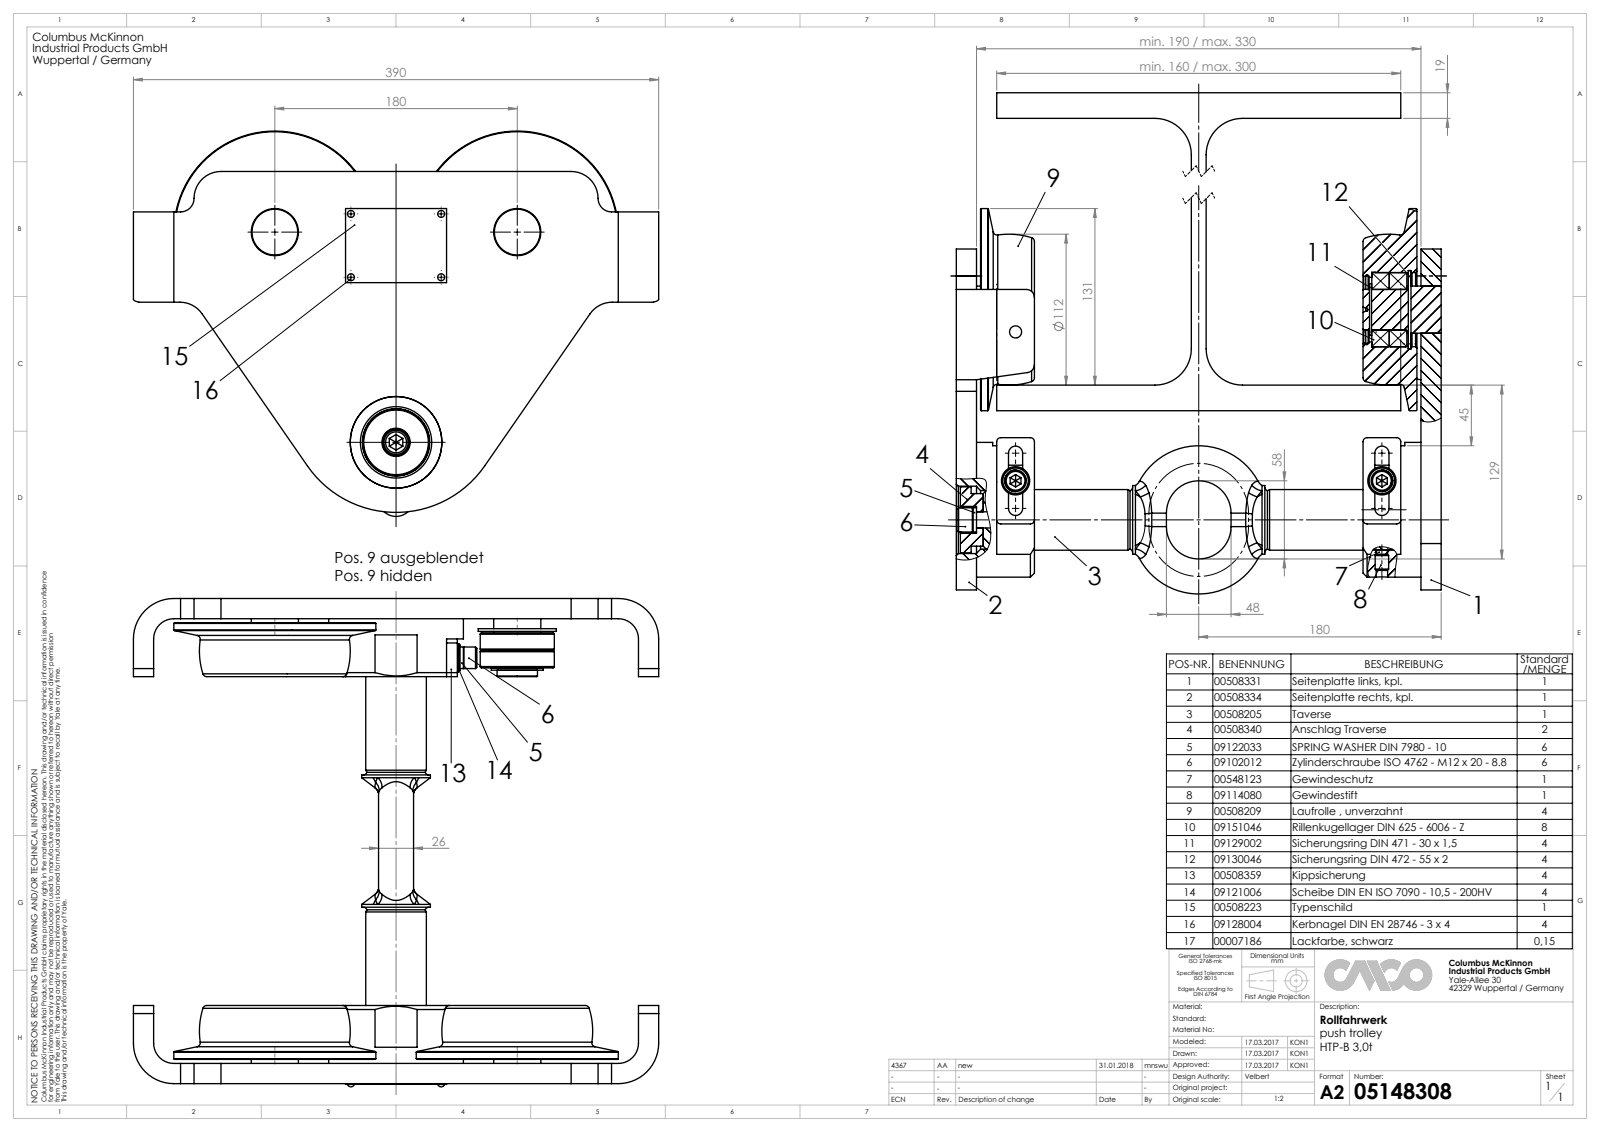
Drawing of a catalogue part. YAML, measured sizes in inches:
part_name: "HTP-B 3,0t"
step_written_by: "SolidWorks 2015 (AUTOMOTIVE_DESIGN)"
units: inches
bodies: {solids: 59, faces: 1232, planar: 406, cylindrical: 450, other: 376}
overall_size: [17.165, 15.748, 14.268]
volume: 656.6
surface_area: 2362
round_holes:
  - {diameter: 0.079, count: 6}
  - {diameter: 0.098, count: 5}
  - {diameter: 0.118, count: 4}
  - {diameter: 0.138, count: 4}
  - {diameter: 0.335, count: 3}
  - {diameter: 0.402, count: 3}
  - {diameter: 0.354, count: 2}
  - {diameter: 0.413, count: 2}
  - {diameter: 1.126, count: 2}
  - {diameter: 1.181, count: 2}
  - {diameter: 1.378, count: 2}
  - {diameter: 1.748, count: 2}
round_bosses_or_shafts:
  - {diameter: 0.205, count: 4}
  - {diameter: 0.394, count: 3}
  - {diameter: 5.906, count: 2}
  - {diameter: 2.283, count: 2}
  - {diameter: 1.52, count: 2}
  - {diameter: 0.827, count: 2}
  - {diameter: 0.63, count: 2}
  - {diameter: 3.937, count: 1}
partial_cylinders:
  - {radius: 0.118, count: 8}
  - {radius: 0.098, count: 5}
  - {radius: 0.079, count: 4}
  - {radius: 0.207, count: 4}
  - {radius: 0.236, count: 4}
  - {radius: 0.591, count: 4}
  - {radius: 0.787, count: 4}
  - {radius: 1.063, count: 4}
face_to_face_distances: [0.748, 11.063, 0.591, 11.811, 6.87, 7.303, 6.28, 6.713, 13.583, 10.315]
hole_center_spacings: [0.347, 1.008, 7.087, 0.661, 0.411, 0.197, 0.246, 0.411]
